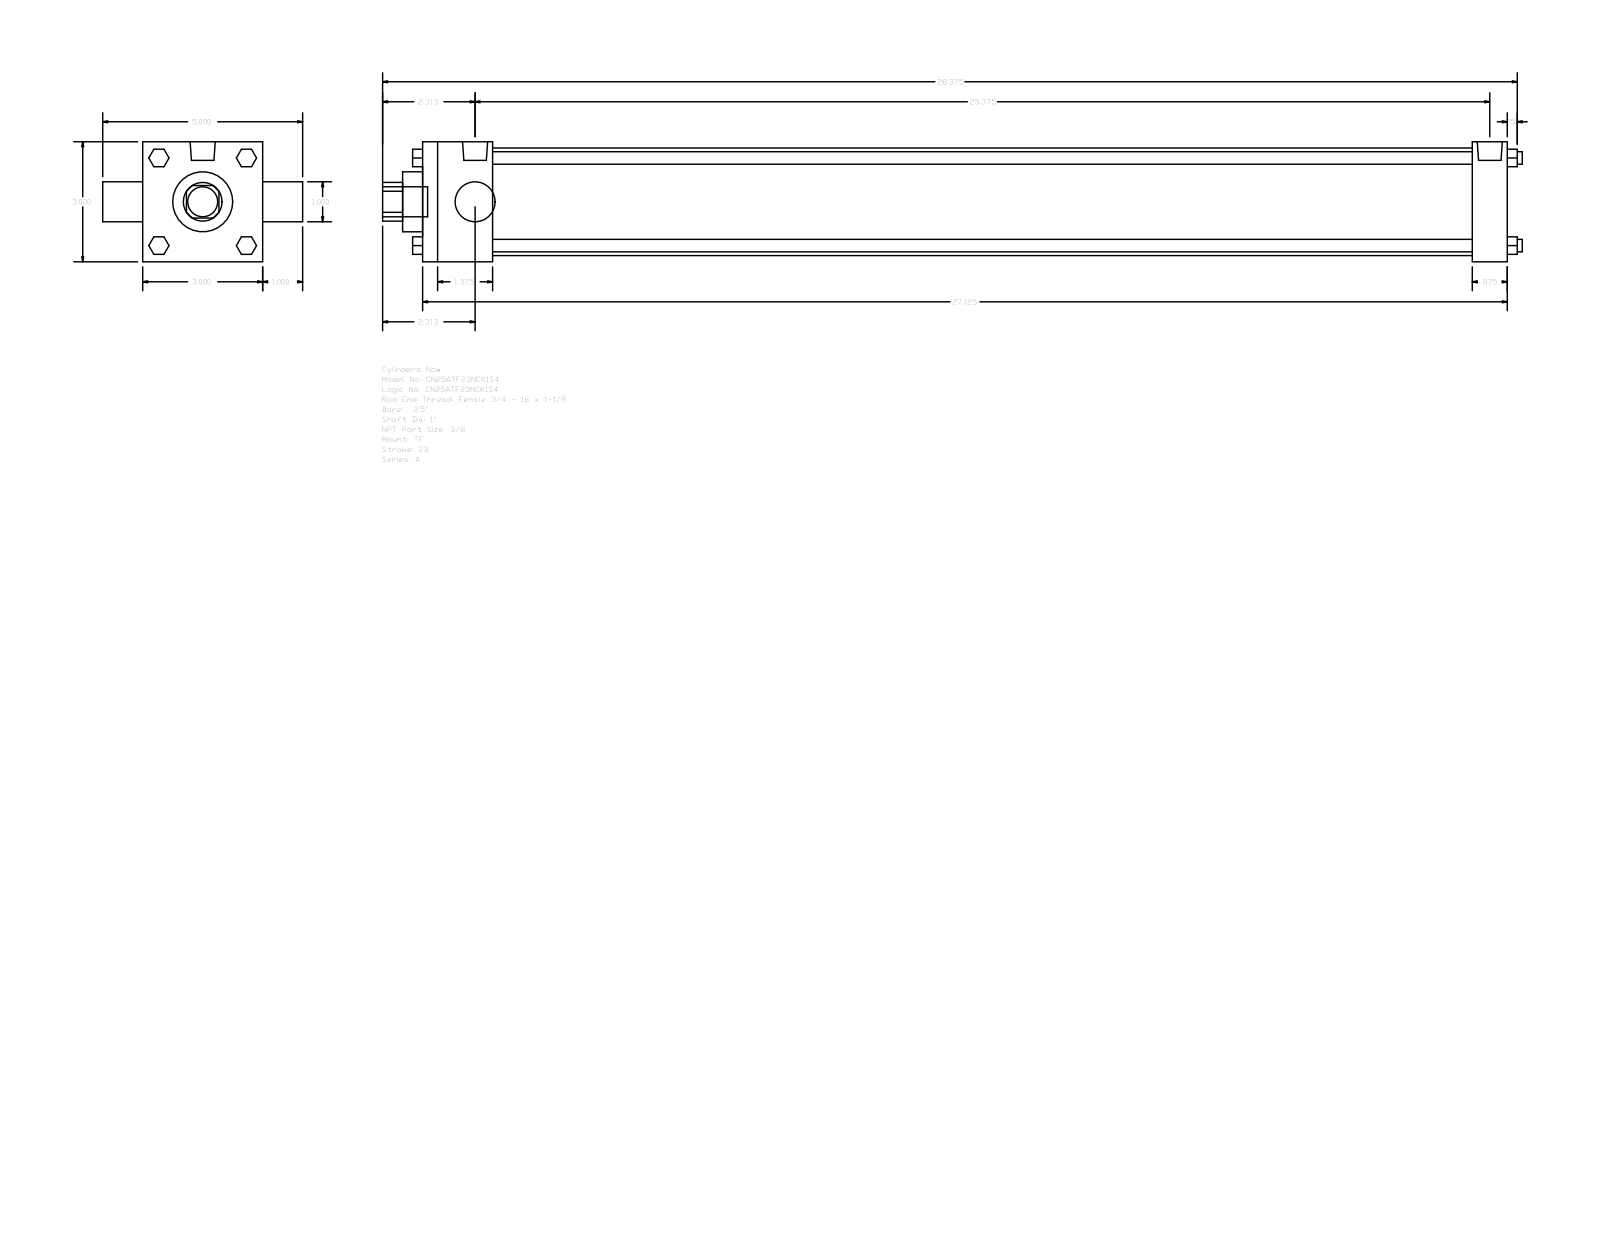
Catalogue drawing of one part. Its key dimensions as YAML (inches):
part_name: "A_TF__0250_1"
step_written_by: "GSSL Pune (CONFIG_CONTROL_DESIGN)"
units: inches
bodies: {solids: 0, faces: 120, planar: 92, cylindrical: 28, other: 0}
overall_size: [28.5, 5, 3]
round_holes:
  - {diameter: 1, count: 2}
  - {diameter: 1.5, count: 1}
  - {diameter: 2.69, count: 1}
round_bosses_or_shafts:
  - {diameter: 0.313, count: 4}
  - {diameter: 0.219, count: 3}
  - {diameter: 0.627, count: 2}
  - {diameter: 0.75, count: 1}
partial_cylinders:
  - {radius: 0.484, count: 1}
face_to_face_distances: [3, 27.125, 1.75, 26.25, 24.5, 25.375, 0.875, 1, 4, 27.625]
